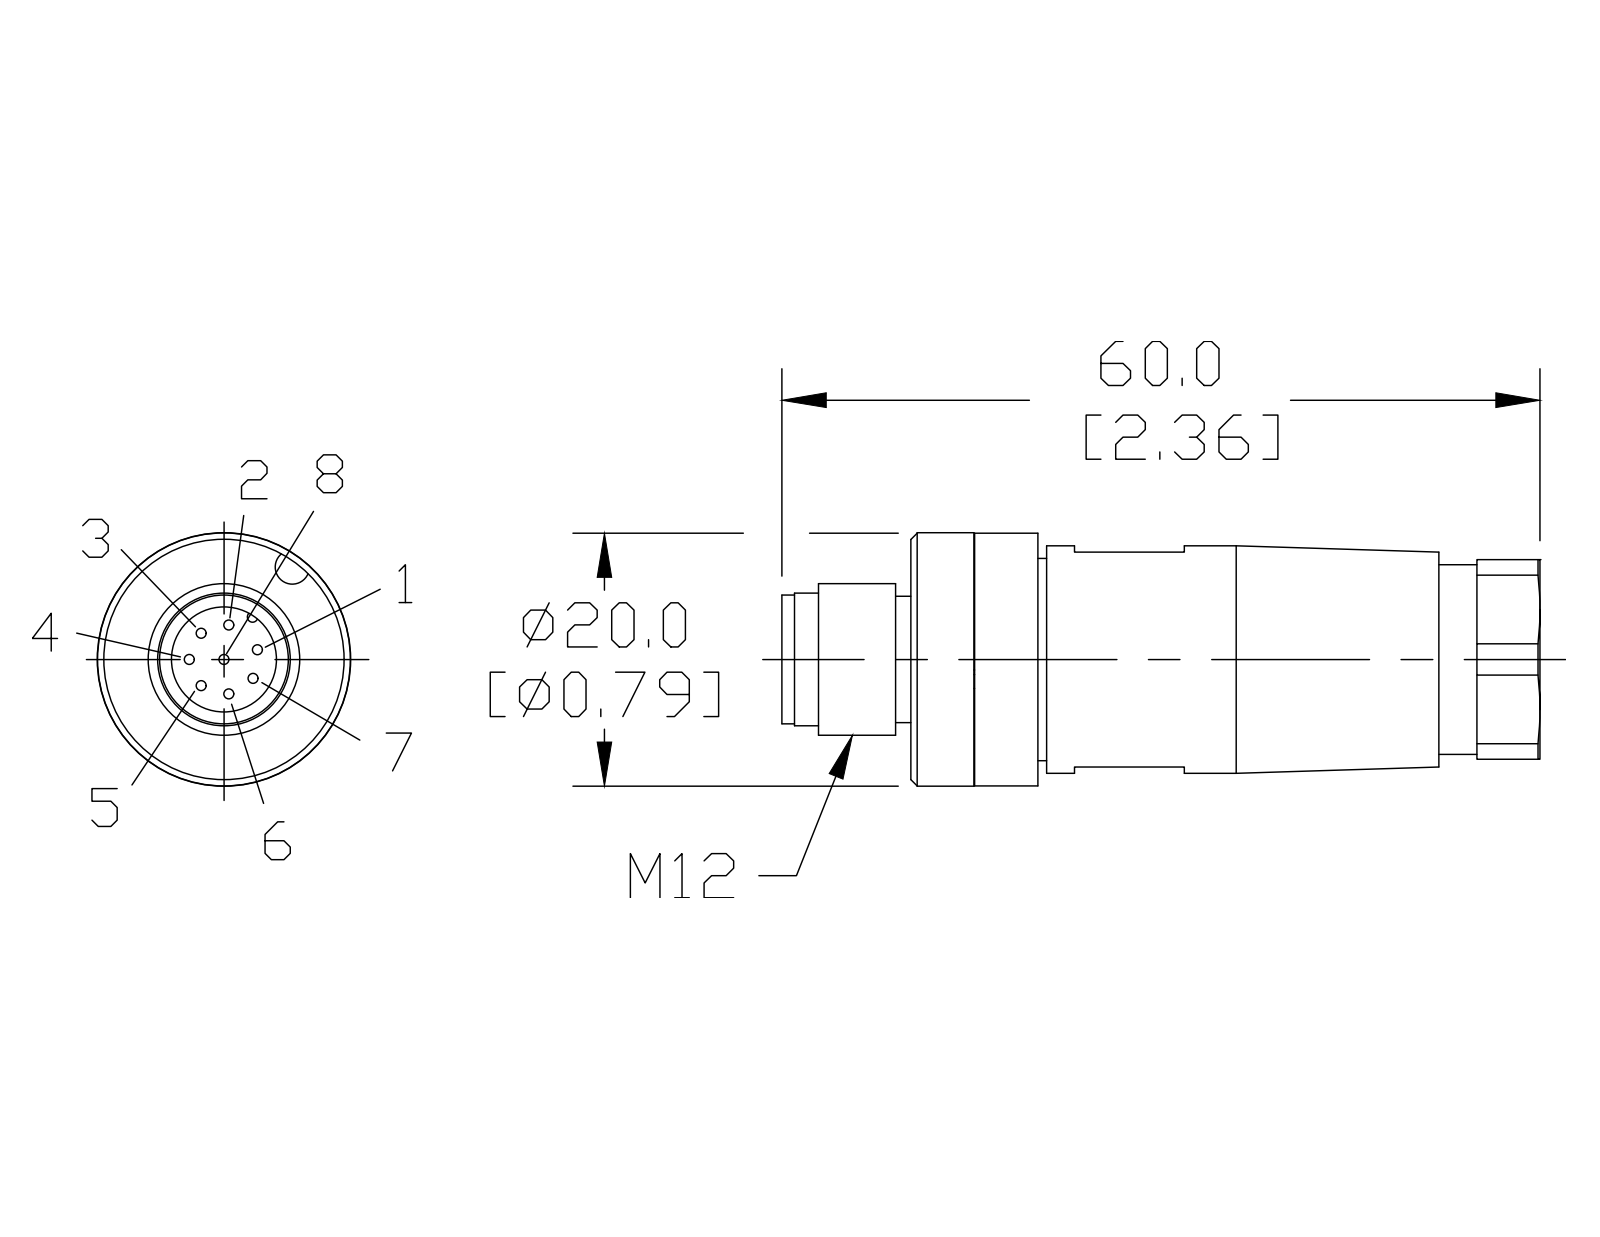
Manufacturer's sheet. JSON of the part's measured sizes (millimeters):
{"part_name": "7000-17301-0000000", "step_written_by": "SolidWorks 2015 (AUTOMOTIVE_DESIGN)", "units": "millimeters", "bodies": {"solids": 1, "faces": 96, "planar": 30, "cylindrical": 48, "other": 18}, "overall_size": [60, 20.05, 20.05], "volume_mm3": 12374, "surface_area_mm2": 5273, "round_holes": [[3, 1], [8.3, 1], [10, 1]], "round_bosses_or_shafts": [[0.8, 8], [20.05, 1], [20, 1], [18, 1], [16, 1], [15, 1], [12, 1], [10.5, 1]], "partial_cylinders_radius": [[0.6, 1], [4.08, 1], [8.5, 1]], "face_to_face_distances": [5, 5.05, 44.8, 39.75, 49.8, 44.75, 10.05, 15.8, 40.3, 35.3]}
